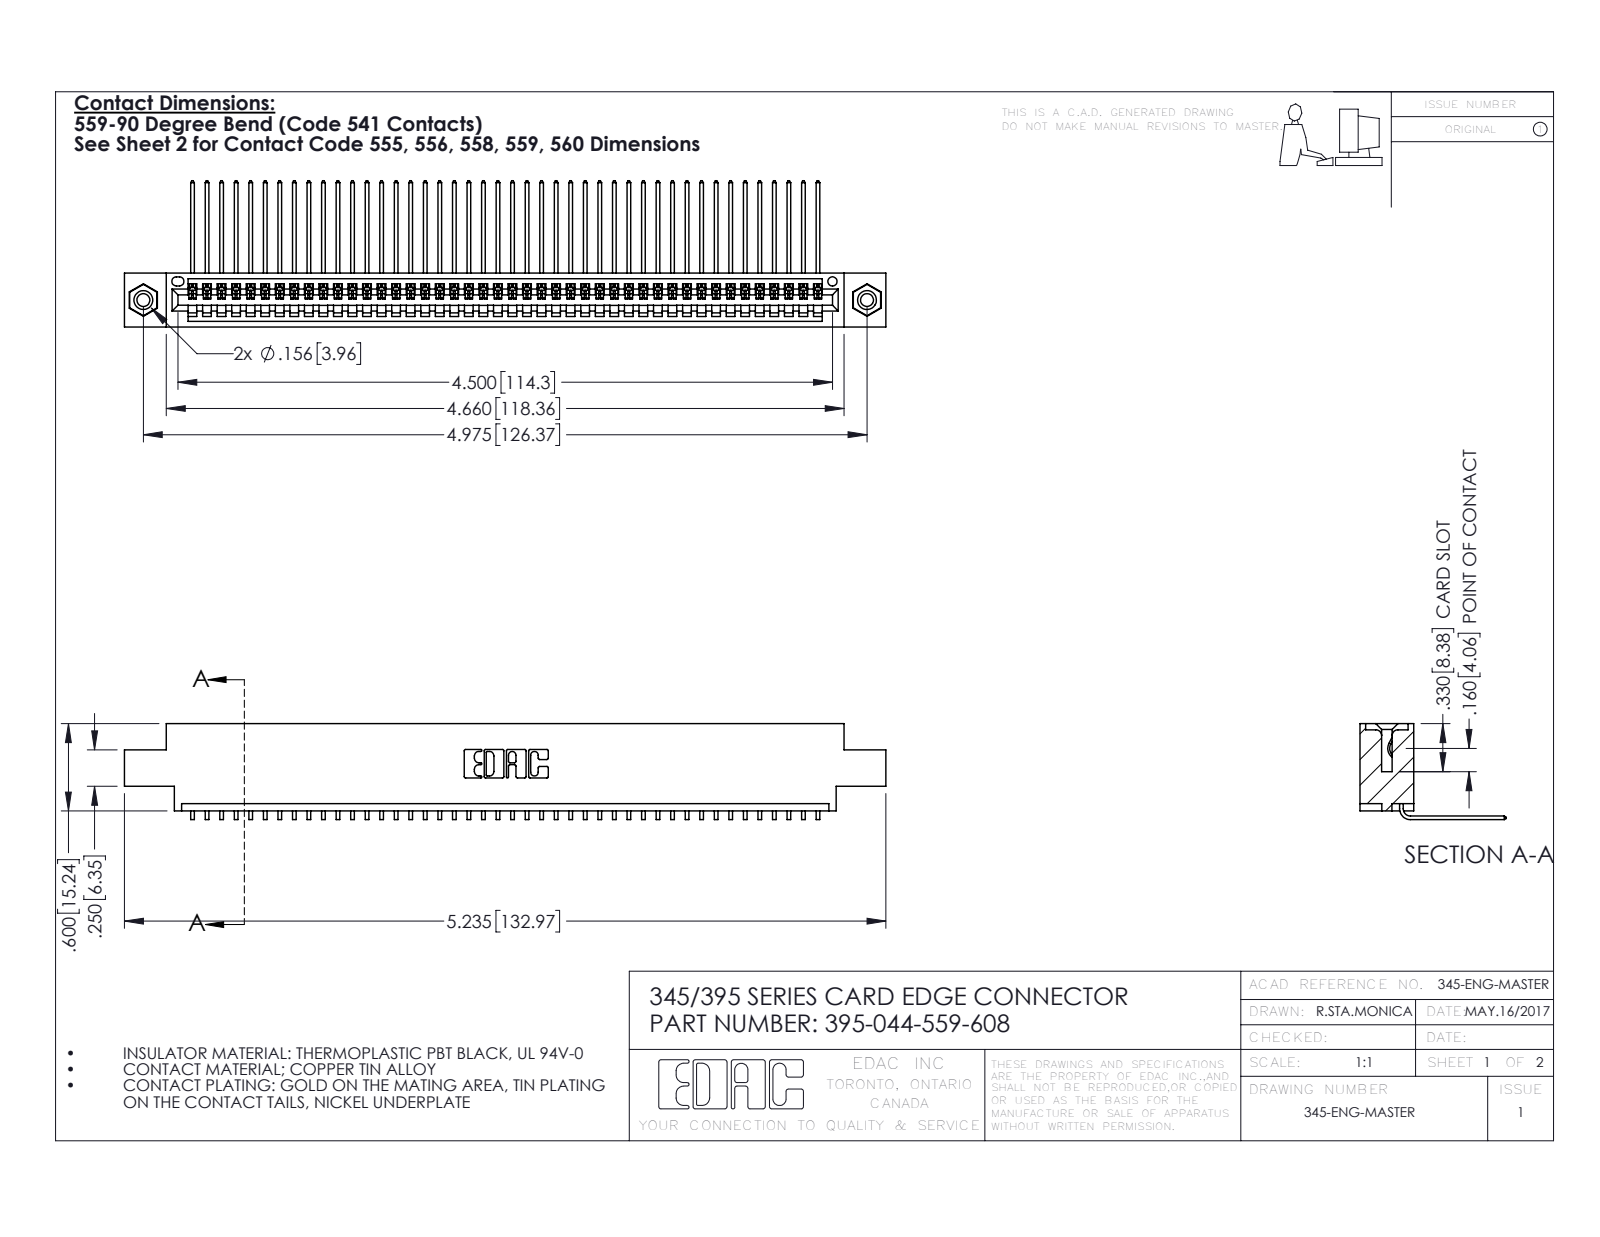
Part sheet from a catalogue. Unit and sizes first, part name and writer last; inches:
Units: inches
Overall size (bounding box): 5.235 × 1.005 × 0.659
Round holes (diameter × count): ⌀0.089 ×2, ⌀0.125 ×2, ⌀0.156 ×2, ⌀0.064 ×1
Round bosses / shafts (diameter × count): ⌀0.155 ×2
Partial cylindrical surfaces — rounded edges, fillets, slot ends (radius × count): R0.006 ×88, R0.01 ×22, R0.007 ×6, R0.031 ×6, R0.026 ×3, R0.031 ×2, R0.04 ×2, R0.014 ×1
Main face-to-face distances: 0.072, 0.298, 0.37, 0.2, 0.098, 0.272, 0.025, 0.225, 0.175, 0.149
Hole centre spacings: 0.27, 4.739, 4.975
Volume: 0.773 in³ · Surface area: 27.71 in²
Bodies: 47 solids, 2830 faces (1964 planar, 850 cylindrical, 16 other)
Part name (STEP PRODUCT): 345 Part_0.170 Offset - 0.156 Dia-TI; 345-250-001_345-250-003-102; 395-044-559-608; 345-292-001_558 559 Tail - 1
STEP written by: SolidWorks 2016 (CONFIG_CONTROL_DESIGN)
